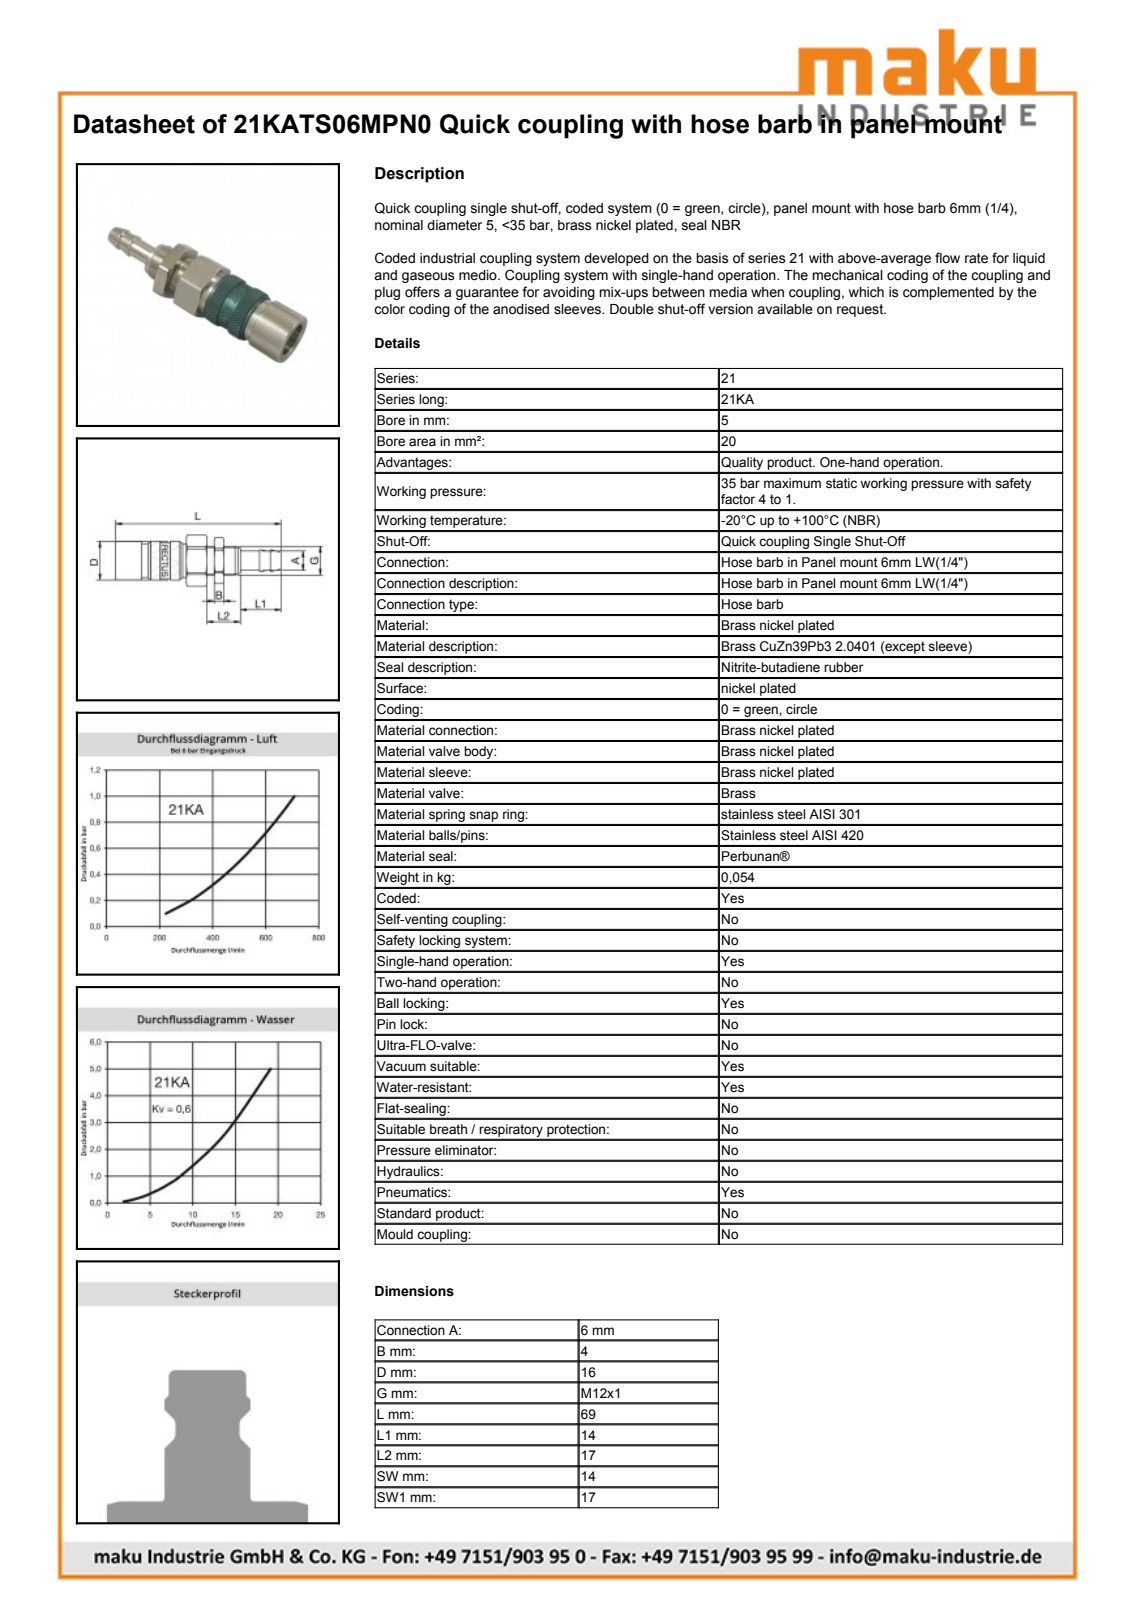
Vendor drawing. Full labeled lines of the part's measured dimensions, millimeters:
Part name (STEP PRODUCT): D110421
STEP written by: Autodesk Inventor 2013 (AUTOMOTIVE_DESIGN)
Units: millimetres
Bodies: 1 solid, 460 faces (172 planar, 64 cylindrical, 224 other)
Overall size (bounding box): 68.91 × 19.06 × 18.95
Volume: 9 073 mm³ · Surface area: 5 160 mm²
Round holes (diameter × count): ⌀10.55 ×1, ⌀12.15 ×1, ⌀14 ×1
Round bosses / shafts (diameter × count): ⌀16.15 ×1, ⌀15.8 ×1, ⌀15.1 ×1, ⌀12.06 ×1, ⌀12 ×1, ⌀10.2 ×1, ⌀6.05 ×1
Partial cylindrical surfaces — rounded edges, fillets, slot ends (radius × count): R7.45 ×1, R9.57 ×1
Main face-to-face distances: 17, 6.55, 2.55, 4, 27.91, 30.46, 34.46, 19.36, 8.55, 11.1
